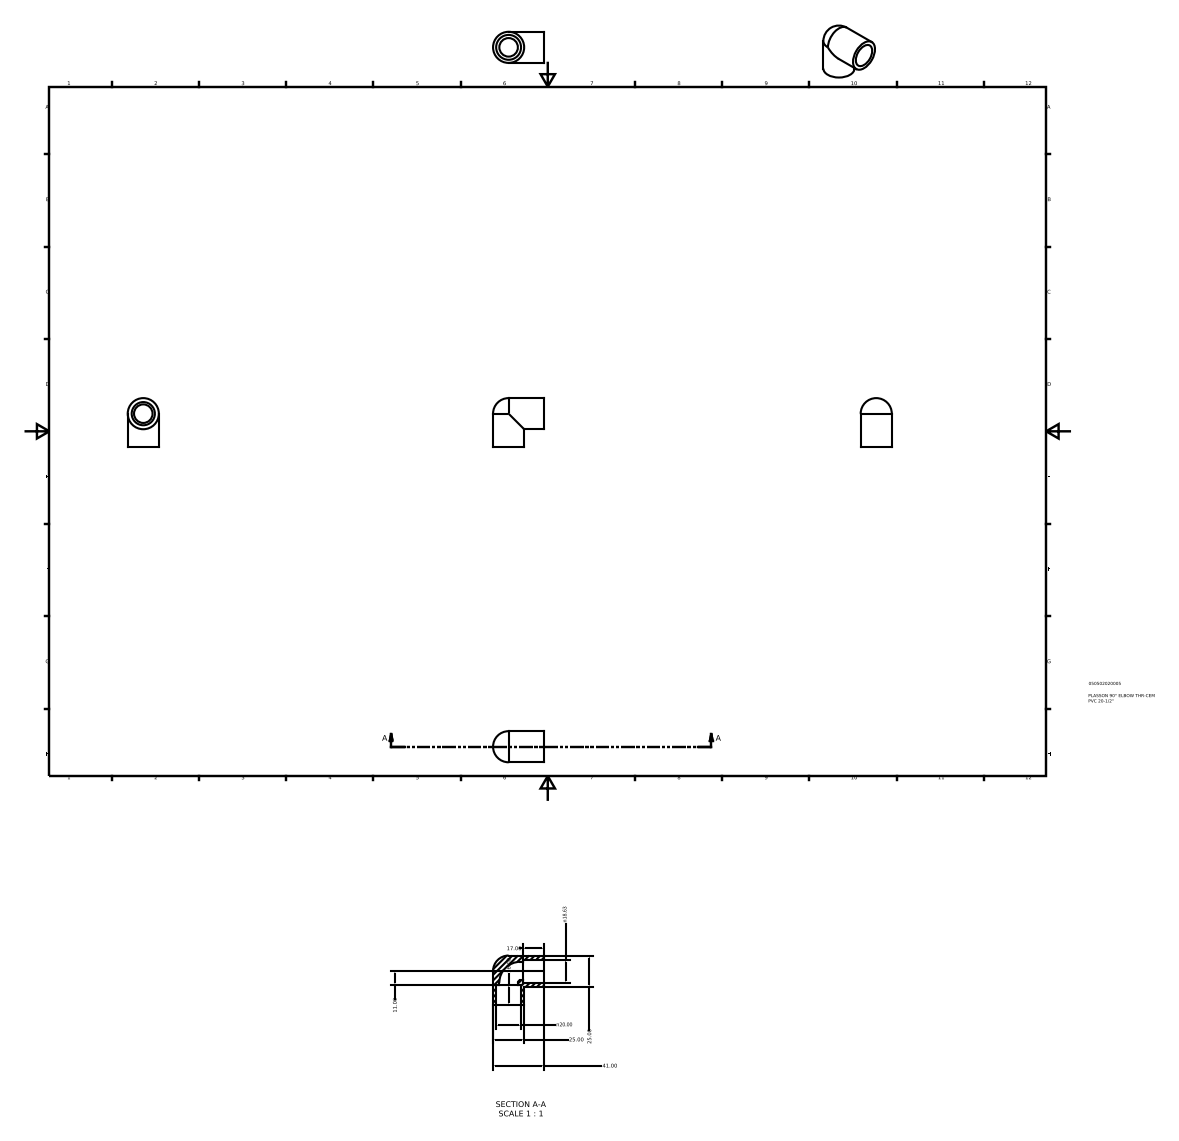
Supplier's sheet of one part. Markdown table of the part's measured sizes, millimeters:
| quantity | value |
| --- | --- |
| part name | 050502020005 |
| STEP written by | Autodesk Inventor 2015 (AUTOMOTIVE_DESIGN) |
| units | millimeters |
| bodies | 1 solid, 12 faces (4 planar, 6 cylindrical, 2 other) |
| overall size | 41 × 39.5 × 25 |
| volume | 13 795 mm³ |
| surface area | 7 724 mm² |
| round holes (diameter × count) | 14.9 × 2, 18.63 × 1, 20 × 1 |
| round bosses / shafts (diameter × count) | 25 × 2 |
| main face-to-face distances | 16, 17 |
